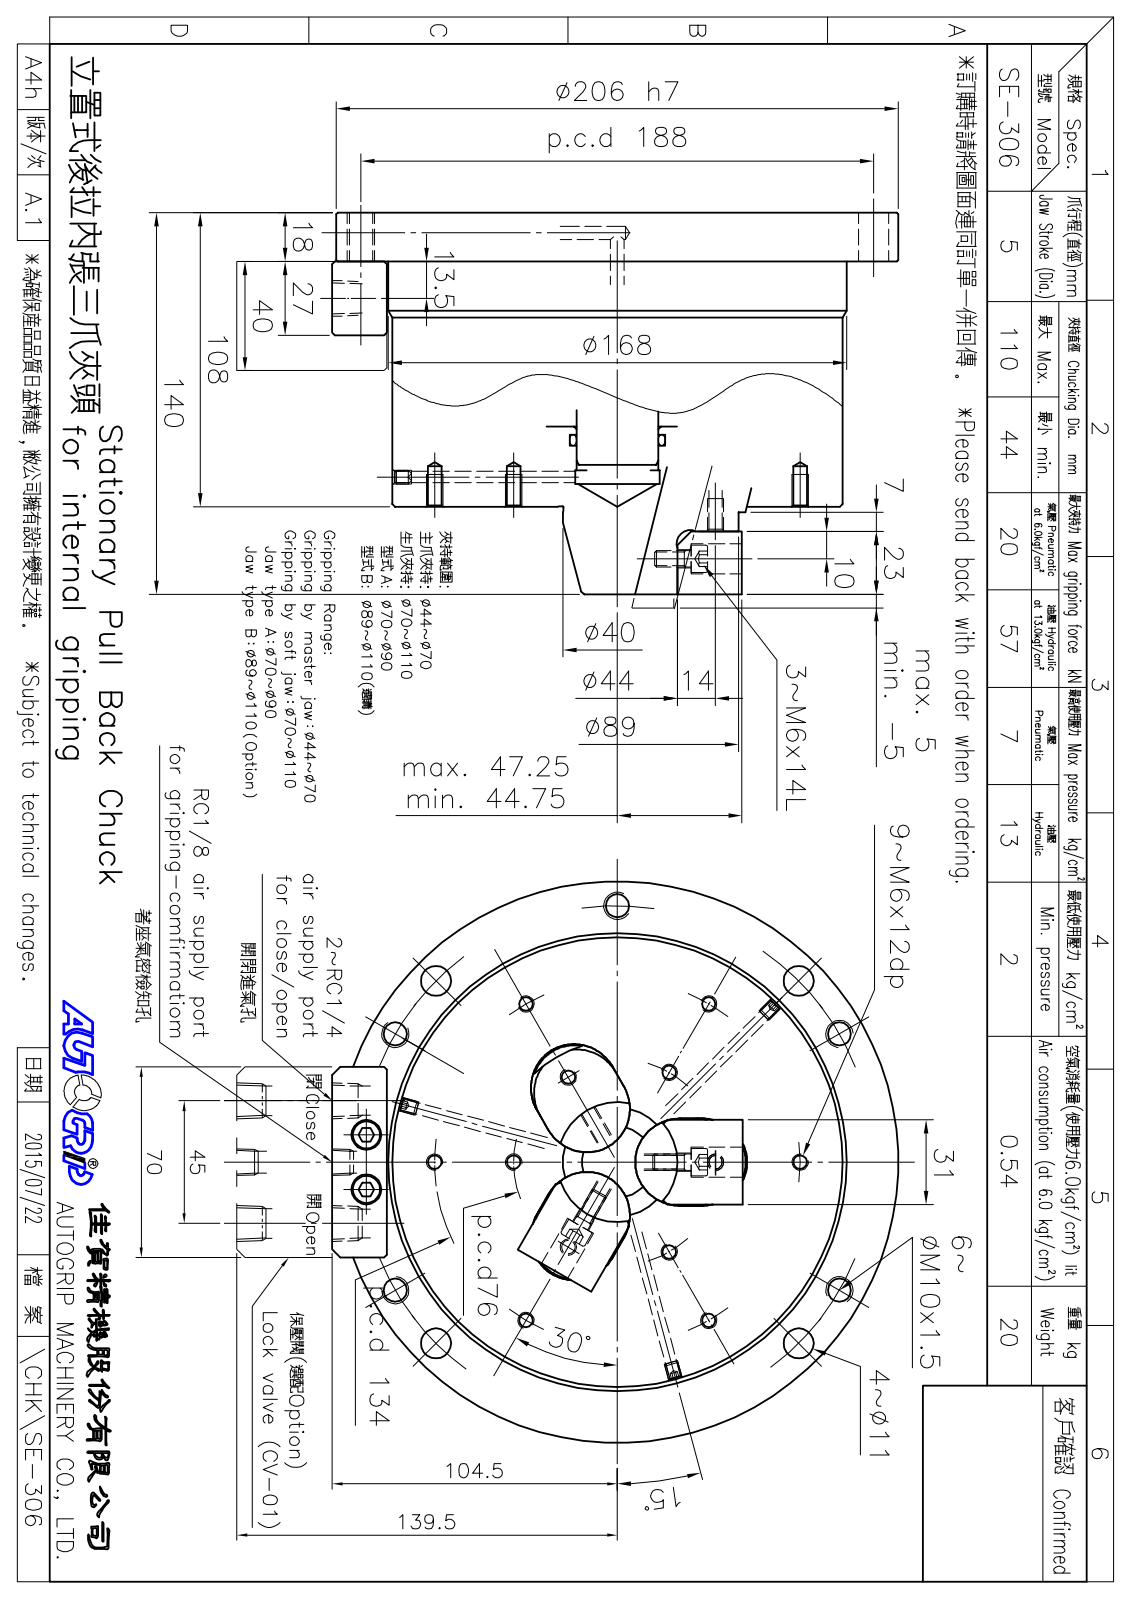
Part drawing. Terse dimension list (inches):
name: 3E-06-05010; CF-SE-306; CF-SU-308-07000; CF-SU-306-05000 (+2 more)
written by: SolidWorks 2016 (CONFIG_CONTROL_DESIGN)
unit: in
bodies: 9 solids, 289 faces (111 planar, 101 cylindrical, 77 other)
size: 8.169 × 8.11 × 5.512
volume: 156.5 in³; area: 390.7 in²
holes: 9× ⌀0.236, 9× ⌀0.433, 6× ⌀0.335, 5× ⌀0.26, 3× ⌀1.26, 2× ⌀0.197, 2× ⌀0.421, 1× ⌀0.323, 1× ⌀3.031, 1× ⌀3.937, 1× ⌀6.614
bosses: 3× ⌀1.26, 1× ⌀8.11, 1× ⌀6.496, 1× ⌀1.957
rounds: 1× R0.787, 1× R0.866
face distances: 0.591, 4.252, 3.661, 0.709, 0.118, 3.543, 0.689, 0.02, 0.571, 4.232
hole spacings: 3.701, 1.935, 2.638, 6.129, 4.544, 2.519, 3.625, 3.992
